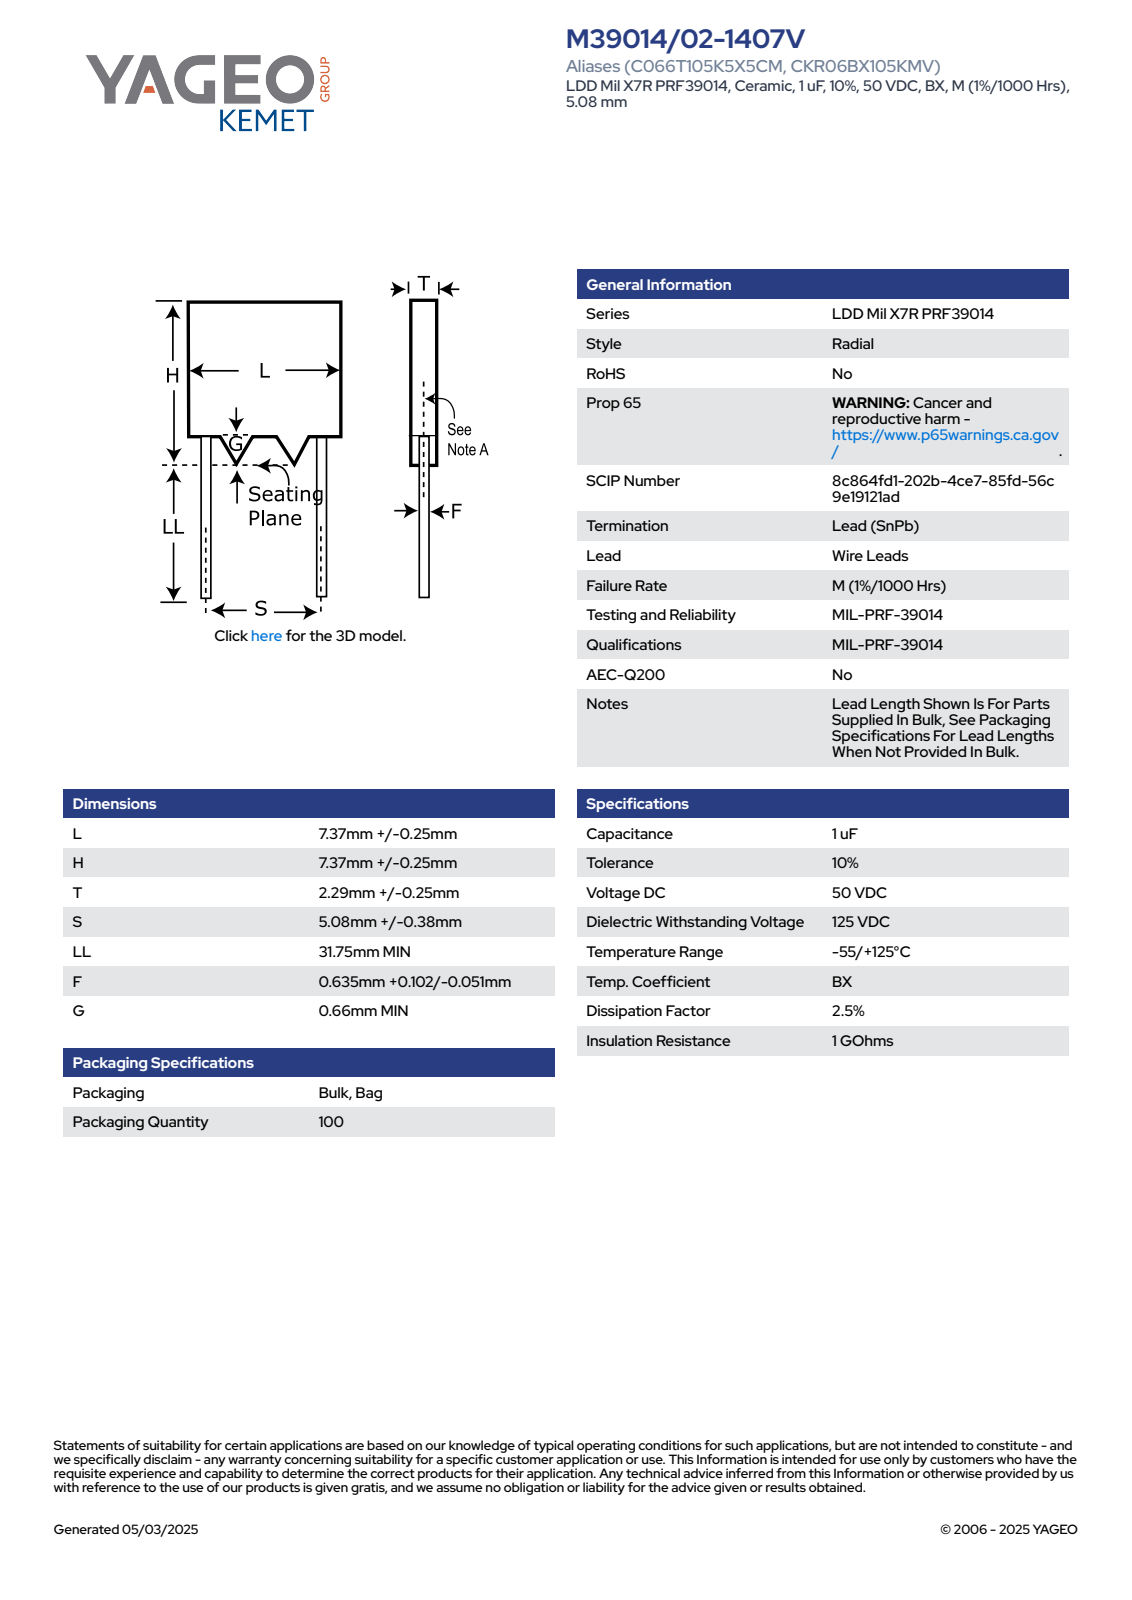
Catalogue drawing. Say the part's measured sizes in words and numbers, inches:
The part is named "CCRM_V_C066_L7.62H7.62T2.54S5.08LL31.75F0.737G0.66". Its 3-D file was written by "SolidWorks 2014 (AUTOMOTIVE_DESIGN)". It is 4 solids with 75 faces: 71 planar, 4 cylindrical and 0 other. Overall it measures 1.514 by 0.3 by 0.1 inches. Its volume is 0.01 cubic inches and its surface area 0.524 square inches. Round bosses or shafts: 2 of diameter 0.029. The main face-to-face distances are 0.1, 0.3, 0.264, 0.079, 1.25, 1.514, 0.048, 1.393, 0.143, 0.121.
